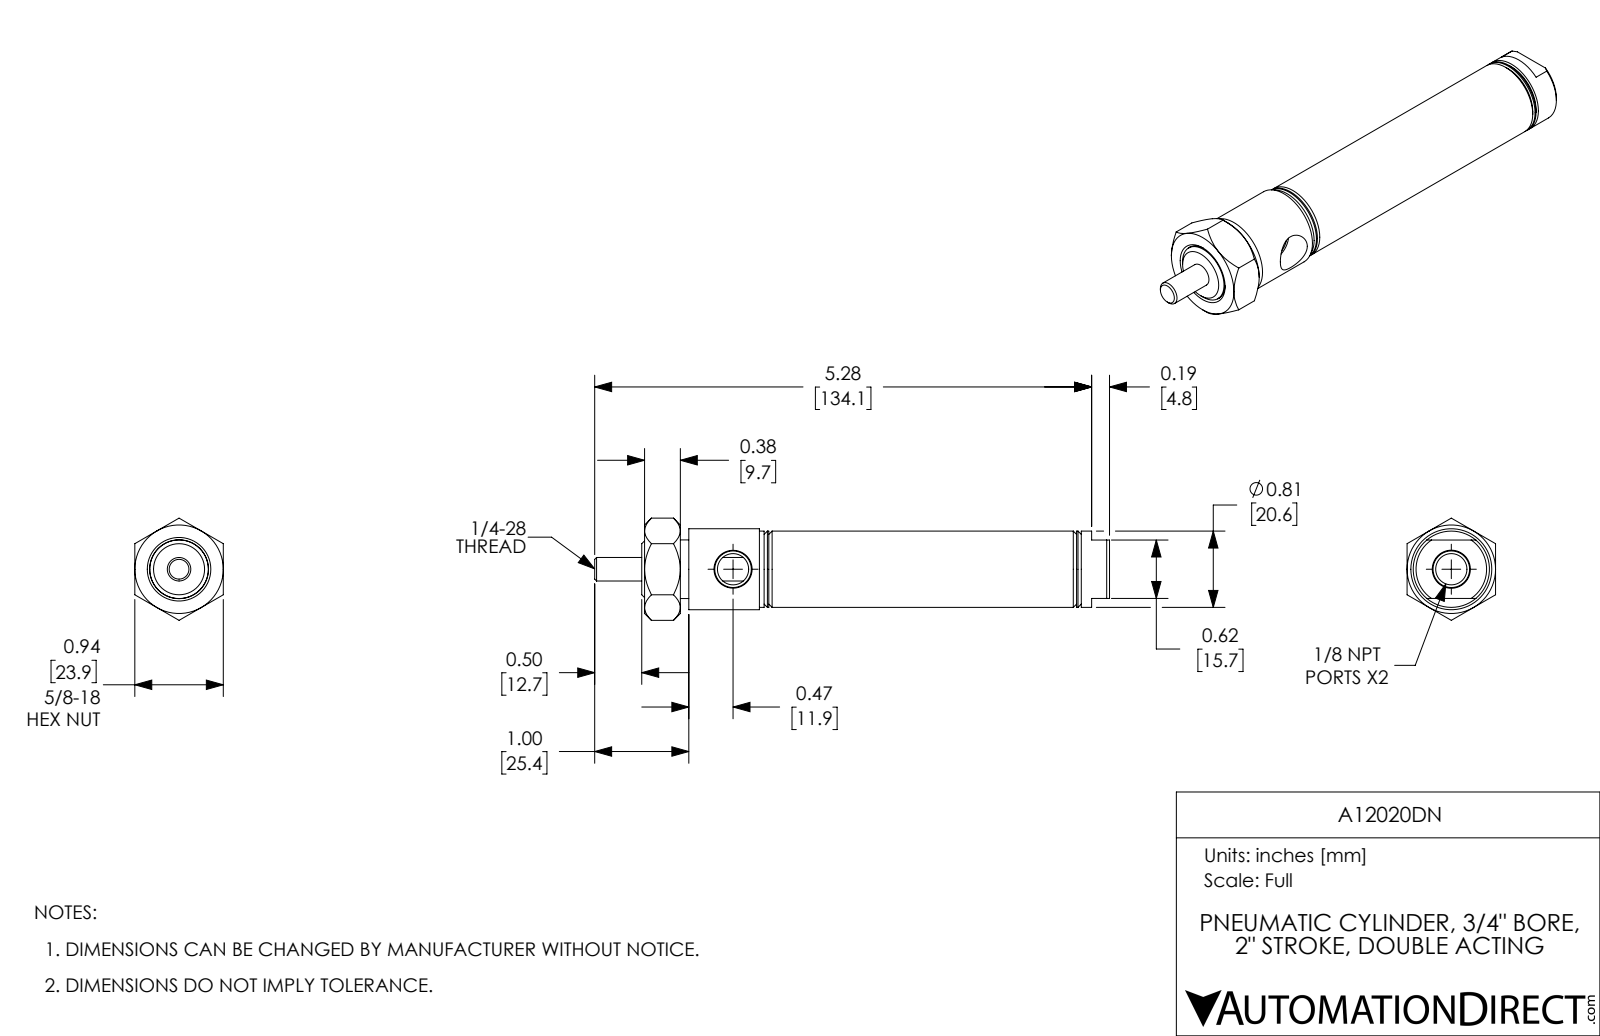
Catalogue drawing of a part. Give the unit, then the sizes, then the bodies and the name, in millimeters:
Units: millimetres
Overall size (bounding box): 138.9 × 27.6 × 23.9
Round holes (diameter × count): ⌀8.4 ×2, ⌀6.4 ×1, ⌀15.9 ×1, ⌀19.1 ×1
Round bosses / shafts (diameter × count): ⌀21.8 ×1, ⌀20.6 ×1, ⌀15.8 ×1
Main face-to-face distances: 88.5, 23.9, 12.7, 25, 37.7, 63.5, 50.8, 90.8, 78.1, 27.3
Volume: 28 810 mm³ · Surface area: 19 930 mm²
Bodies: 3 solids, 94 faces (27 planar, 28 cylindrical, 39 other)
Part name (STEP PRODUCT): A12020DN; A12020DN_Mounting Nut_D-9; A12020DN-Rod; A12020DN-MainBody
STEP written by: SolidWorks 2017 (AUTOMOTIVE_DESIGN)
